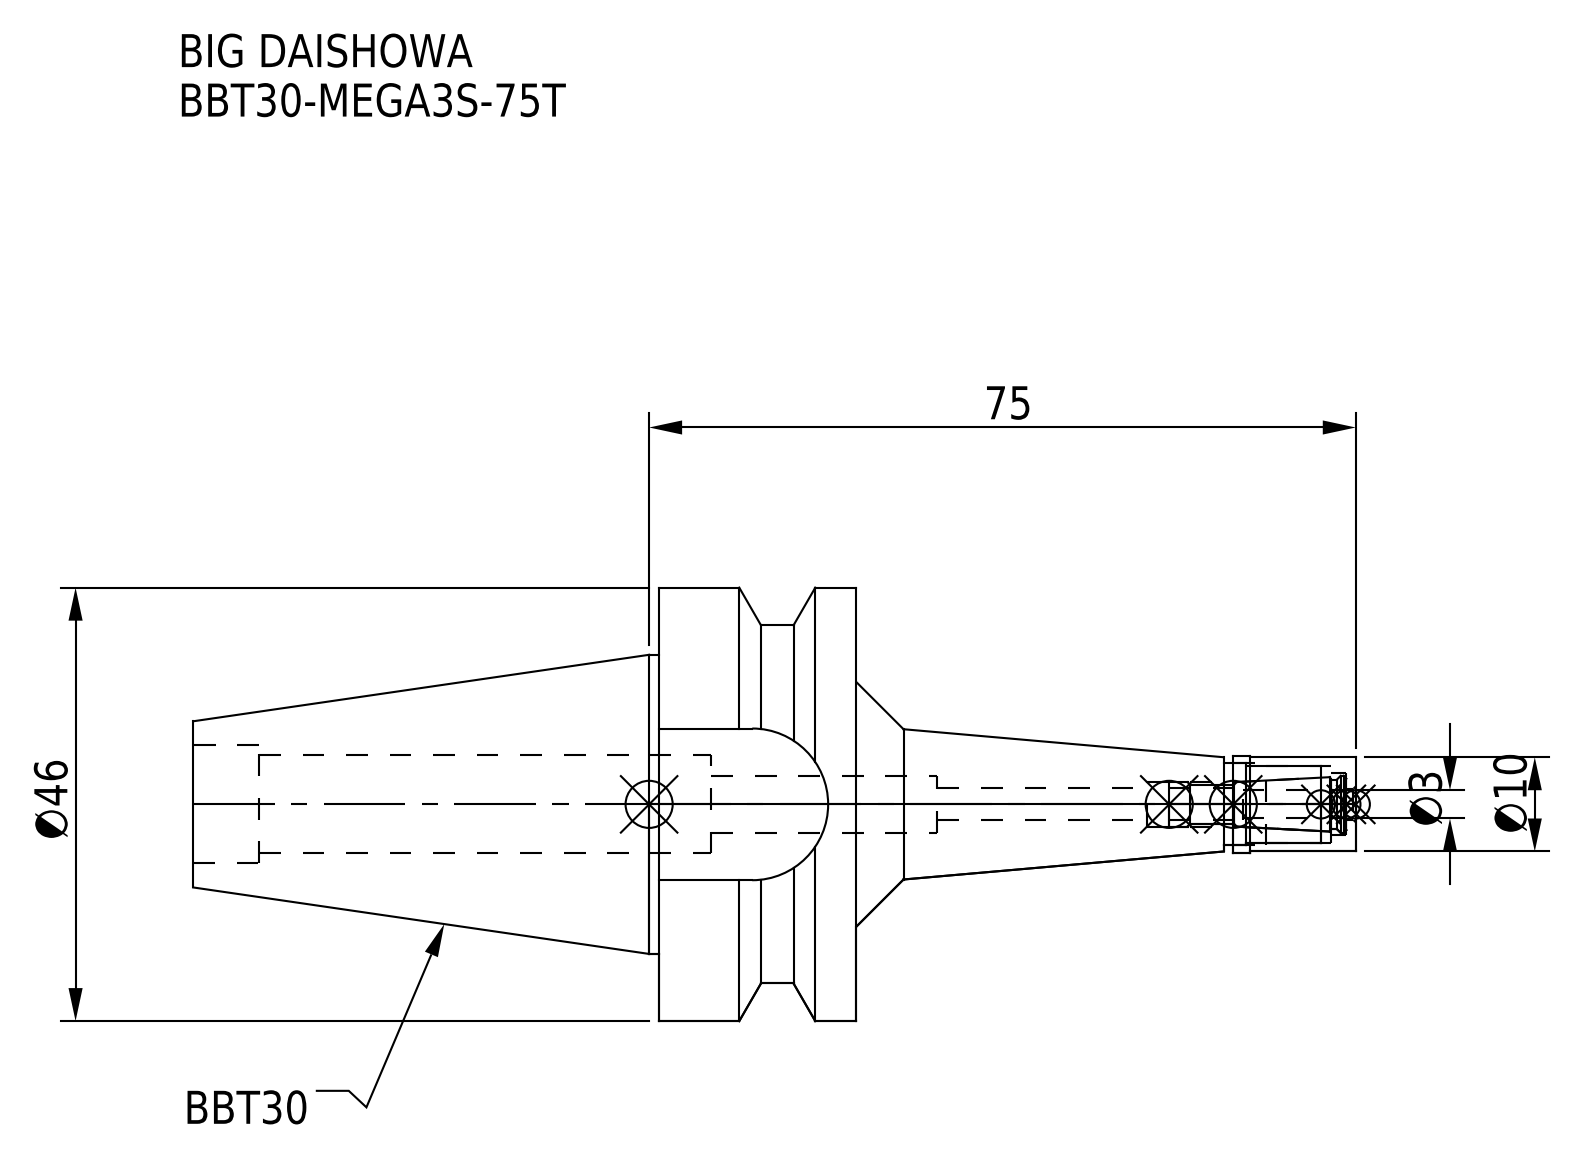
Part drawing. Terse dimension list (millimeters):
name: BBT30-MEGA3S-75T_1.stp; BBT30-MEGA3S-75T-FreeParts; BBT30-MEGA3S-75T.stp; BBT30MS03075T-030_ASM.stp (+3 more)
written by: SolidWorks 2019 (CONFIG_CONTROL_DESIGN)
unit: mm
bodies: 2 solids, 74 faces (22 planar, 38 cylindrical, 14 other)
size: 123.4 × 46 × 46
volume: 54 940 mm³; area: 15 574 mm²
holes: 1× ⌀3.3, 1× ⌀3.4, 1× ⌀4.7, 1× ⌀6, 1× ⌀6.6, 1× ⌀8.2, 1× ⌀8.7, 1× ⌀10.4, 1× ⌀12.5
bosses: 1× ⌀46, 1× ⌀31.75, 1× ⌀10.3, 1× ⌀10
rounds: 1× R8.05, 1× R19
face distances: 21, 32.6, 70.4, 49.4, 16.1, 53, 74, 123.4, 68.4, 15.4
